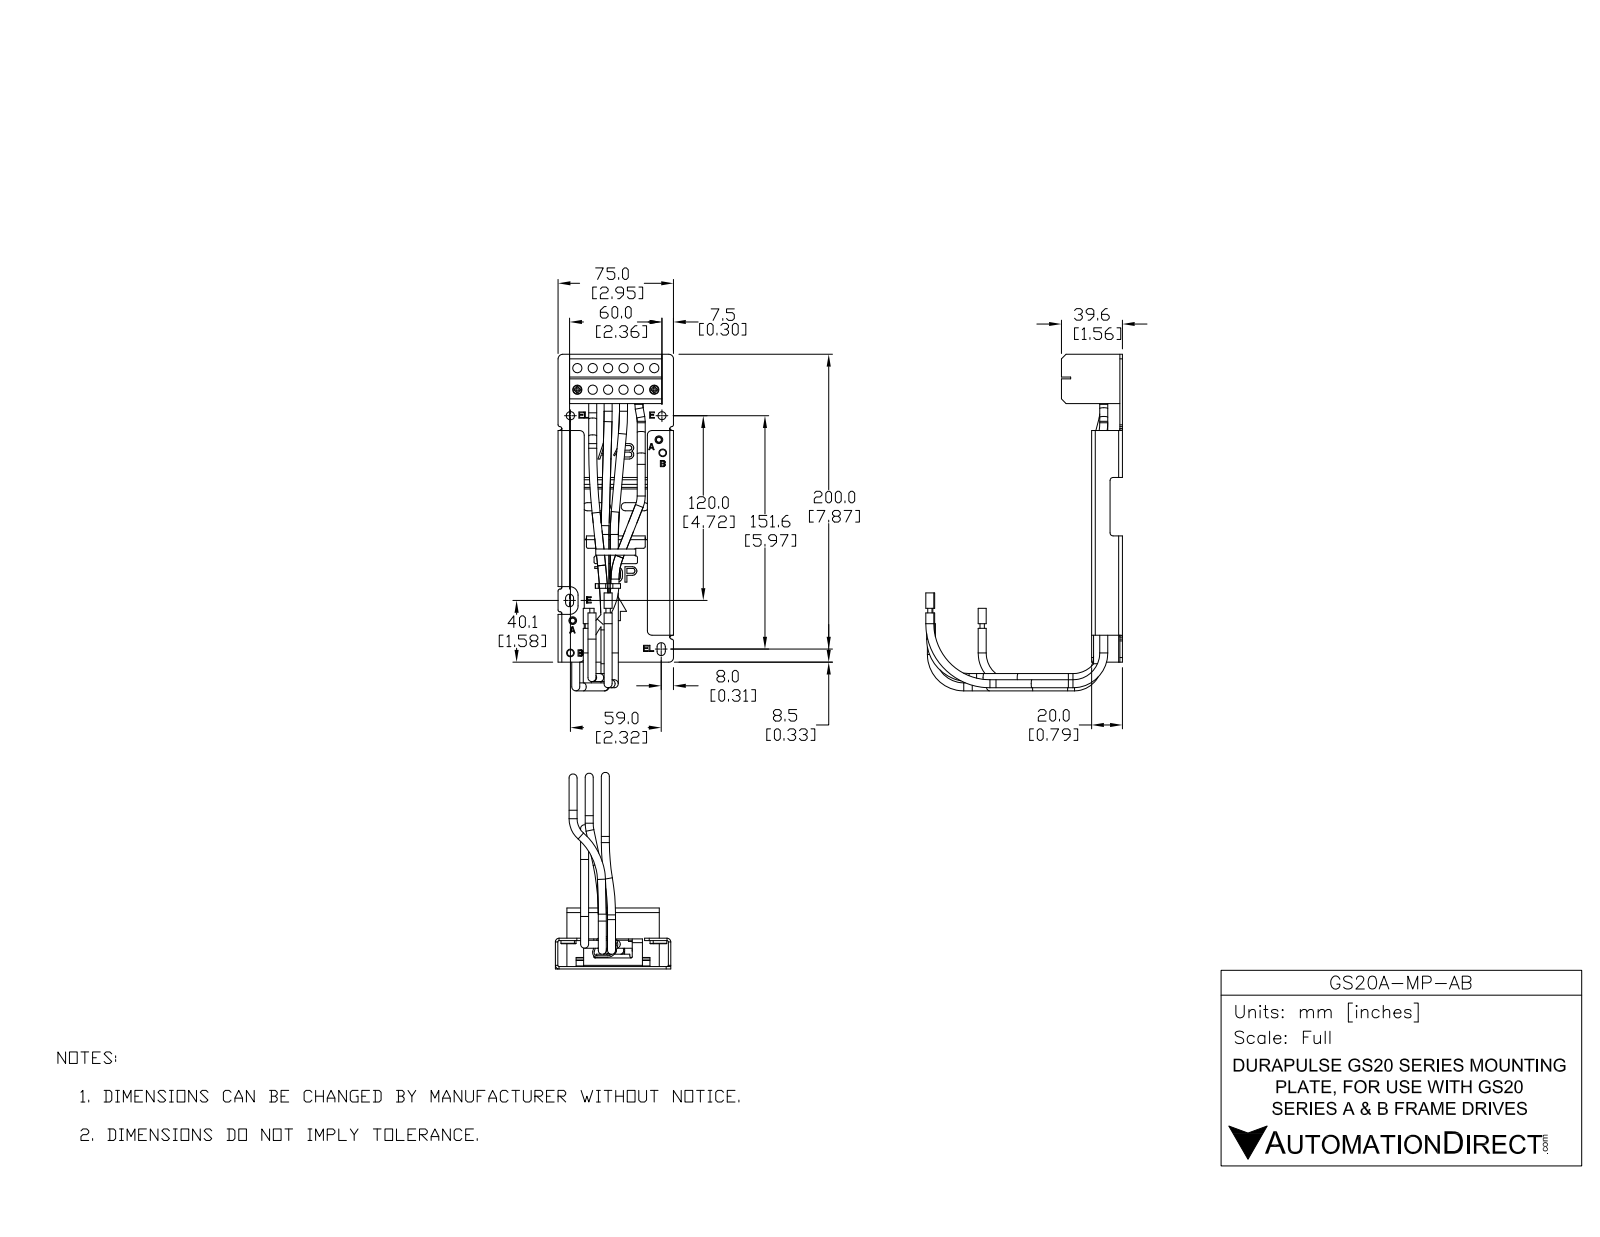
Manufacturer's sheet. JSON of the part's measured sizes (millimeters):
{"part_name": "MKM-MAPB-PD-3D00 R1 fXT", "step_written_by": "SolidWorks 2017 (AUTOMOTIVE_DESIGN)", "units": "millimeters", "bodies": {"solids": 16, "faces": 1132, "planar": 631, "cylindrical": 257, "other": 244}, "overall_size": [218.6, 127.7, 75], "volume_mm3": 117600, "surface_area_mm2": 88060, "round_holes": [[6, 12], [5, 4], [3, 2], [3.3, 2], [4.1, 2], [5.5, 2], [5.2, 1], [5.4, 1]], "round_bosses_or_shafts": [[5.2, 31], [2.8, 8], [8.7, 2], [7.9, 2], [7.5, 2], [6.6, 2], [6.3, 2], [5.4, 2]], "partial_cylinders_radius": [[1, 12], [3, 12], [0.8, 10], [2, 7], [2.4, 6], [2.6, 6], [0.5, 5], [1.2, 5]], "face_to_face_distances": [1.6, 18.4, 20, 16.8, 73.4, 7.5, 67.5, 5.9, 65.9, 32], "hole_center_spacings": [10, 17.2, 20, 24.4, 14, 30, 33.1, 40]}
